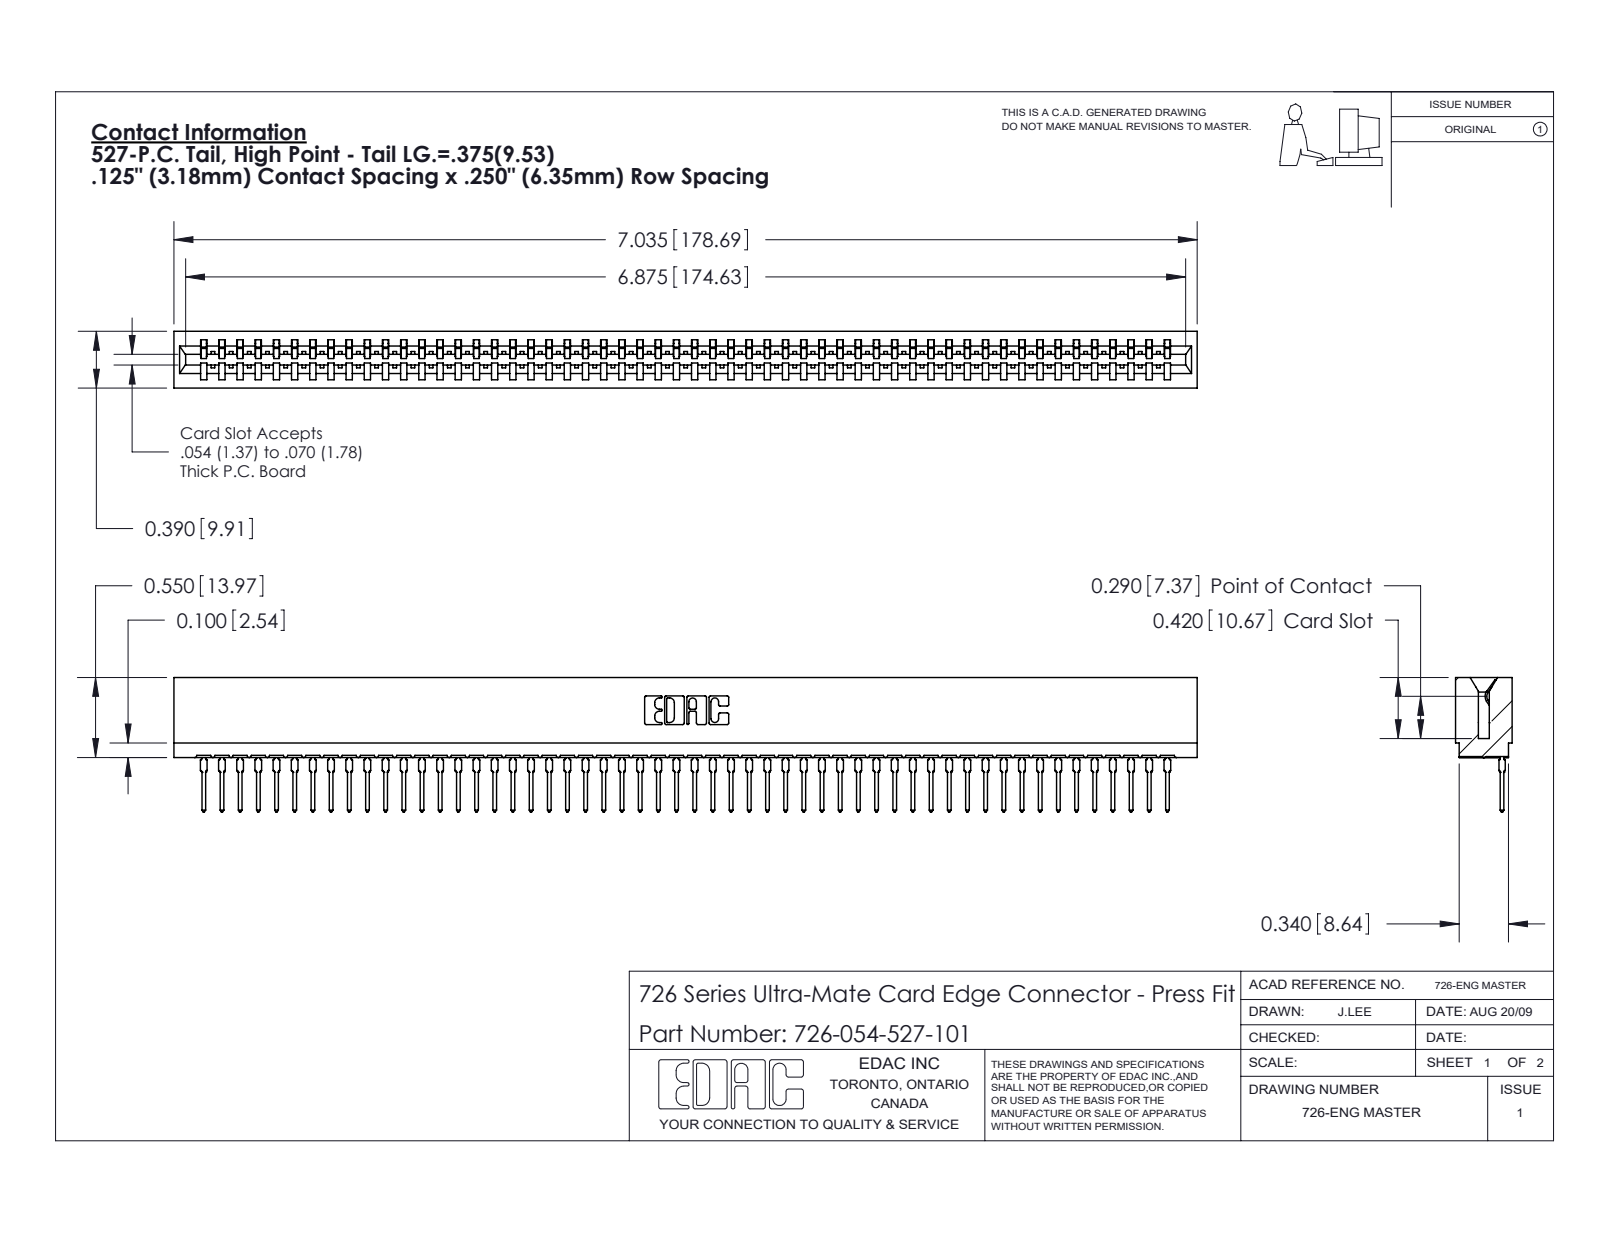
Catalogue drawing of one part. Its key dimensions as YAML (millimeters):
part_name: "746-292-001_527; 726-054-527-101; 726 Part_.515 Slot Depth - 01"
step_written_by: "SolidWorks 2020 (CONFIG_CONTROL_DESIGN)"
units: millimeters
bodies: {solids: 55, faces: 5929, planar: 3457, cylindrical: 1068, other: 1404}
overall_size: [178.7, 23.5, 9.9]
volume: 15900
surface_area: 24810
partial_cylinders:
  - {radius: 0.5, count: 108}
  - {radius: 0.4, count: 55}
  - {radius: 0.3, count: 22}
  - {radius: 0.2, count: 6}
  - {radius: 0.8, count: 6}
  - {radius: 0.1, count: 4}
  - {radius: 0.3, count: 4}
  - {radius: 0.7, count: 3}
face_to_face_distances: [1.4, 8.5, 9.9, 0.6, 7.8, 6.4, 7, 2.1, 9.3, 0.8]
